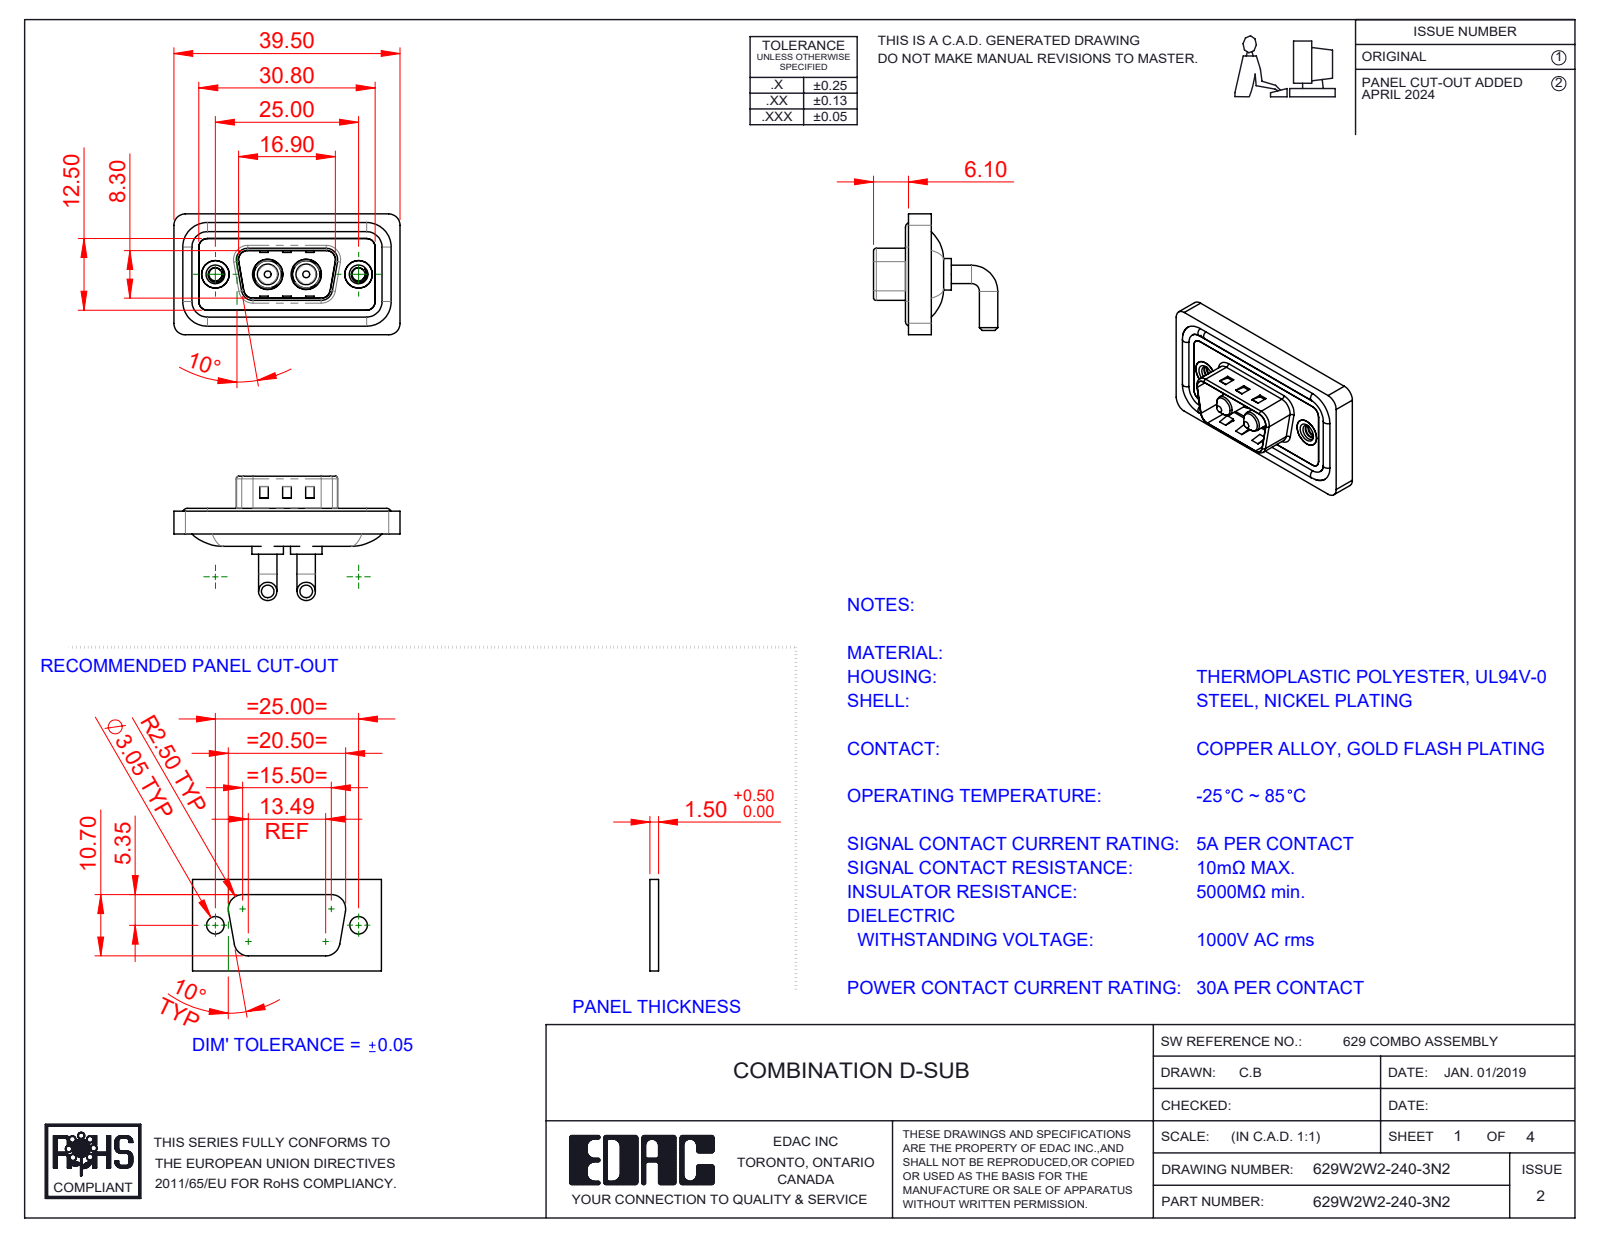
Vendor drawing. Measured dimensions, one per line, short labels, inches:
name: 629Combo Threaded Rivet_2; 629Combo Waterproof Housing_09 Contacts; Power Pin_30A RA; 629W2W2-140-3N2 (+3 more)
written by: SolidWorks 2023 (CONFIG_CONTROL_DESIGN)
unit: in
bodies: 11 solids, 497 faces (165 planar, 222 cylindrical, 110 other)
size: 1.555 × 0.854 × 0.831
volume: 0.284 in³; area: 11.17 in²
holes: 2× ⌀0.089, 2× ⌀0.157, 2× ⌀0.189, 2× ⌀0.191, 2× ⌀0.197, 2× ⌀0.209
bosses: 4× ⌀0.126, 4× ⌀0.063, 2× ⌀0.217, 2× ⌀0.205, 2× ⌀0.193, 2× ⌀0.187, 2× ⌀0.148, 2× ⌀0.142
rounds: 18× R0.059, 18× R0.079, 8× R0.02, 8× R0.063, 4× R0.01, 4× R0.024, 4× R0.026, 4× R0.035
face distances: 0.016, 0.114, 0.043, 0.031, 0.083, 0.098, 0.122, 0.063, 0.177, 0.059
hole spacings: 0.36, 0.624, 0.265, 0.984
